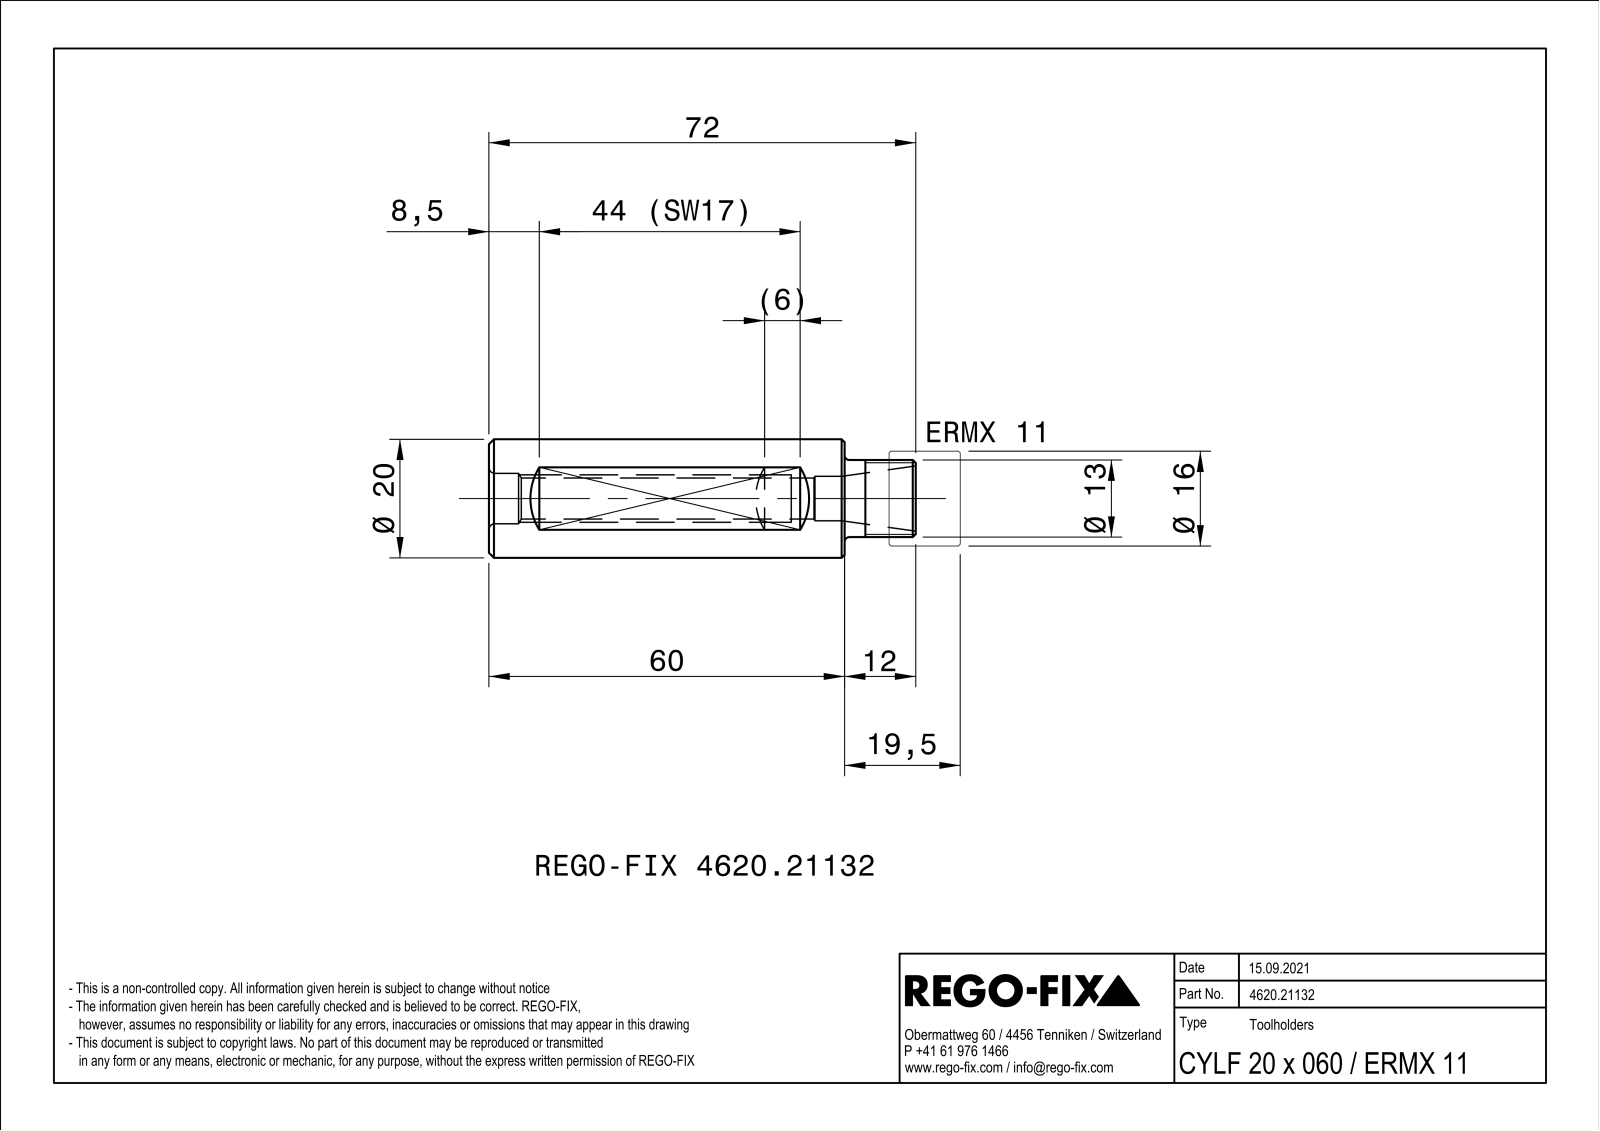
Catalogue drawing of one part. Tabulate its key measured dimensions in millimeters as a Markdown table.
| quantity | value |
| --- | --- |
| part name | NOCUT |
| STEP written by | SIEMENS PLM Software Solid Edge ST10 (AUTOMOTIVE_DESIGN) |
| units | millimeters |
| bodies | 1 solid, 25 faces (9 planar, 7 cylindrical, 9 other) |
| overall size | 72 × 20 × 20 |
| volume | 16 631 mm³ |
| surface area | 6 343 mm² |
| round holes (diameter × count) | 6.92 × 1, 7.5 × 1, 8.5 × 1 |
| round bosses / shafts (diameter × count) | 20 × 1, 13 × 1 |
| main face-to-face distances | 60, 17, 19.09, 7.78, 12, 72 |
